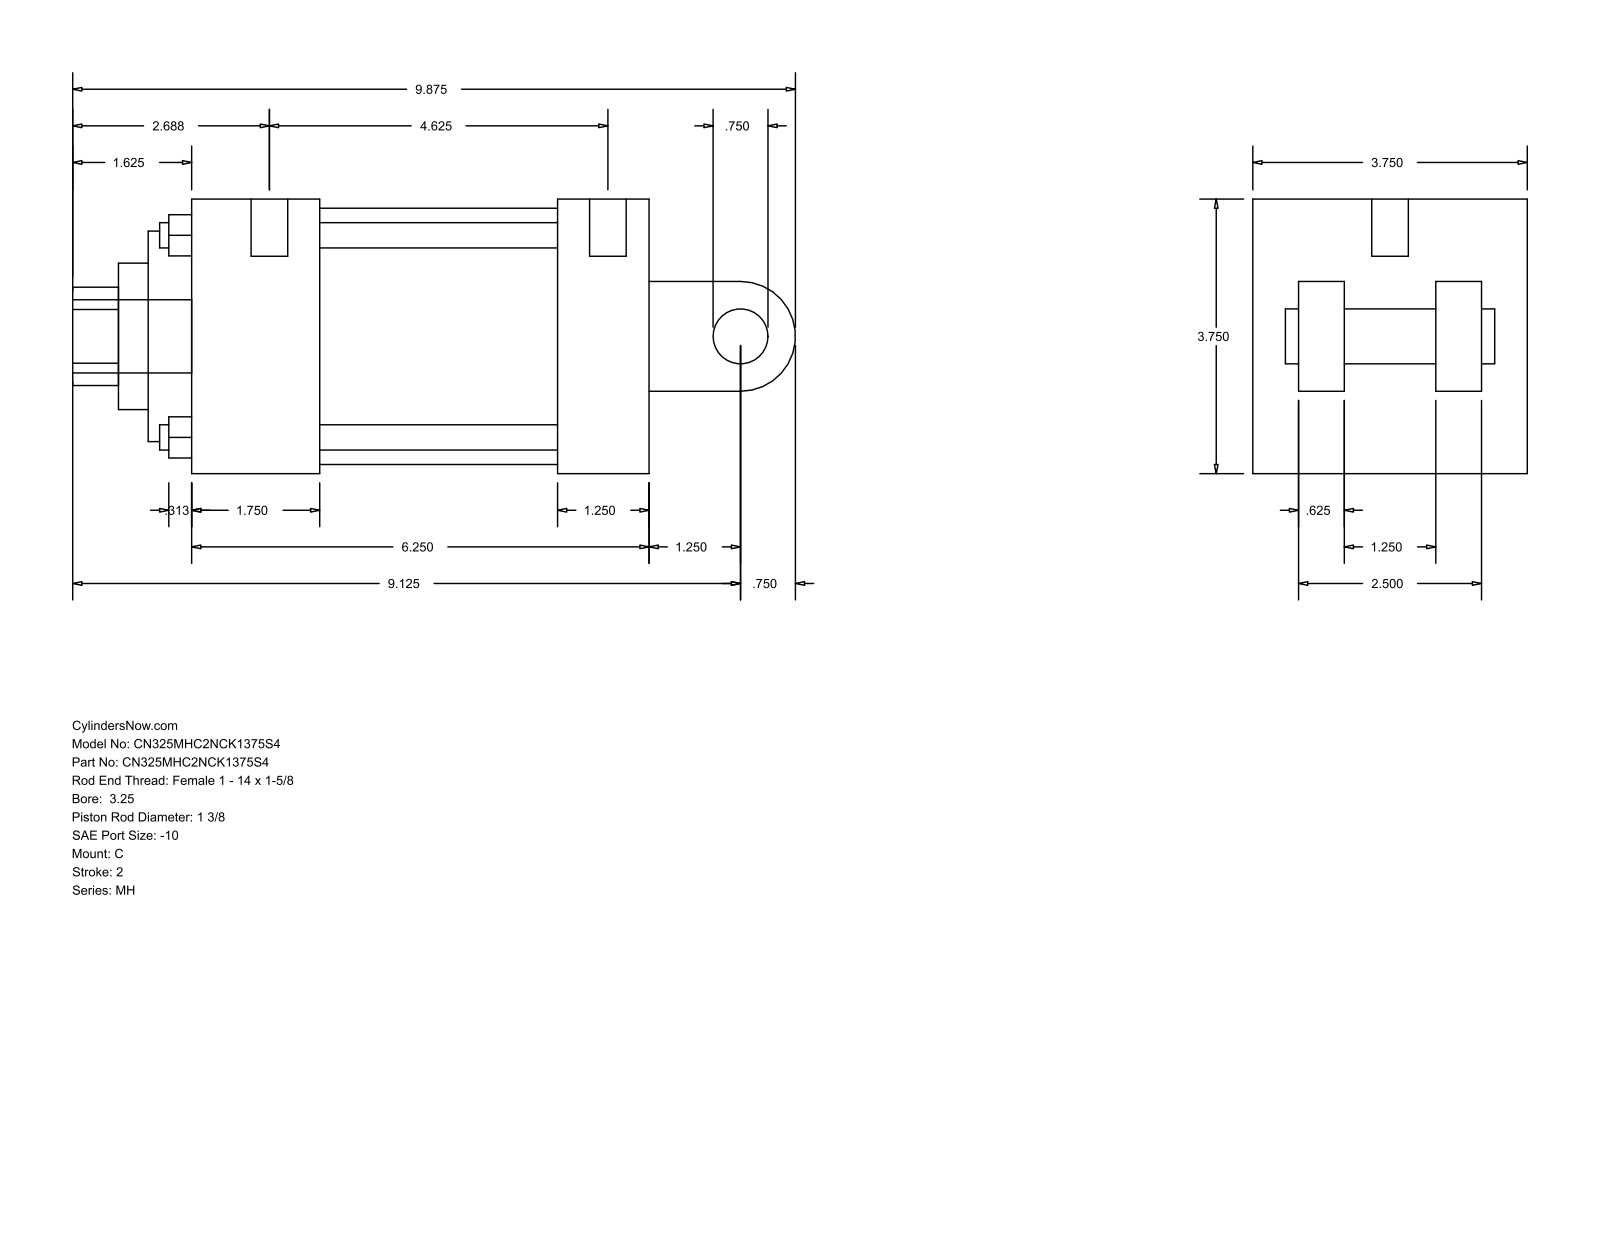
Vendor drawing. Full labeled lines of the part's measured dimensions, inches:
Part name (STEP PRODUCT): MH_C__0325_1.375
STEP written by: GSSL Pune (CONFIG_CONTROL_DESIGN)
Units: inches
Bodies: 0 solids, 101 faces (71 planar, 30 cylindrical, 0 other)
Overall size (bounding box): 9.875 × 3.75 × 3.75
Round holes (diameter × count): ⌀0.345 ×4, ⌀0.219 ×2, ⌀0.5 ×1, ⌀1.375 ×1, ⌀2 ×1, ⌀2.875 ×1, ⌀3.5 ×1
Round bosses / shafts (diameter × count): ⌀0.219 ×2, ⌀1 ×1, ⌀0.75 ×1, ⌀0.5 ×1
Partial cylindrical surfaces — rounded edges, fillets, slot ends (radius × count): R0.672 ×1, R0.75 ×1
Main face-to-face distances: 3.75, 0.625, 6.25, 2.5, 3.125, 1.25, 1.875, 1.75, 5, 3.25
Hole centre spacings: 1.952, 2.76, 3.903, 0.187
